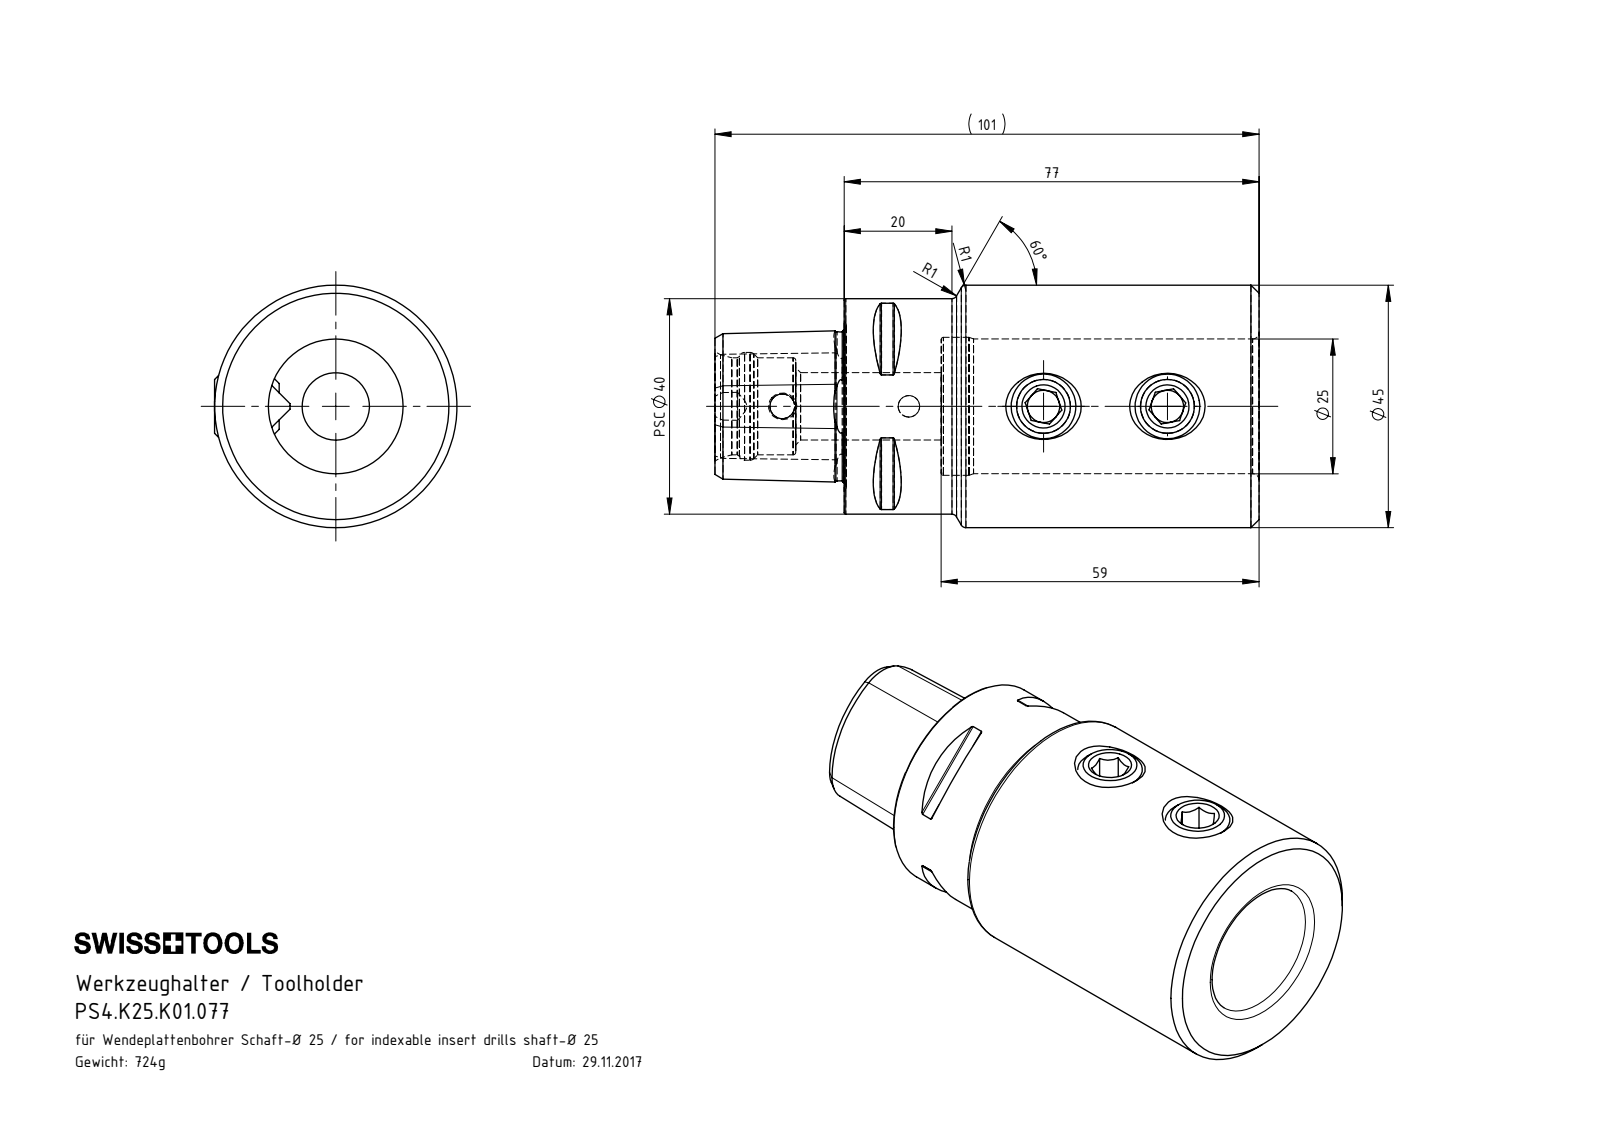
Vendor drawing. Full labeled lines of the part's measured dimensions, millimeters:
Part name (STEP PRODUCT): PS4-K25.K01.077_A; PS4.K25.K01.077; K32-ER1.012.012; K32-ER2.012.014_PreviewCfg
STEP written by: SolidWorks 2017 (AUTOMOTIVE_DESIGN)
Units: millimetres
Bodies: 3 solids, 145 faces (48 planar, 26 cylindrical, 71 other)
Overall size (bounding box): 101 × 45 × 45
Volume: 91 902 mm³ · Surface area: 23 705 mm²
Round holes (diameter × count): ⌀6 ×2, ⌀11 ×2, ⌀4 ×1, ⌀4.6 ×1, ⌀12.5 ×1, ⌀18 ×1, ⌀20 ×1, ⌀25 ×1, ⌀25.6 ×1
Round bosses / shafts (diameter × count): ⌀12 ×2, ⌀45 ×1, ⌀40 ×1
Partial cylindrical surfaces — rounded edges, fillets, slot ends (radius × count): R0.3 ×8, R3 ×1
Main face-to-face distances: 77, 18, 59, 24, 42, 101, 15.52, 6, 35.3, 15
Hole centre spacings: 23, 23.5, 25, 48, 48.5, 71.5
